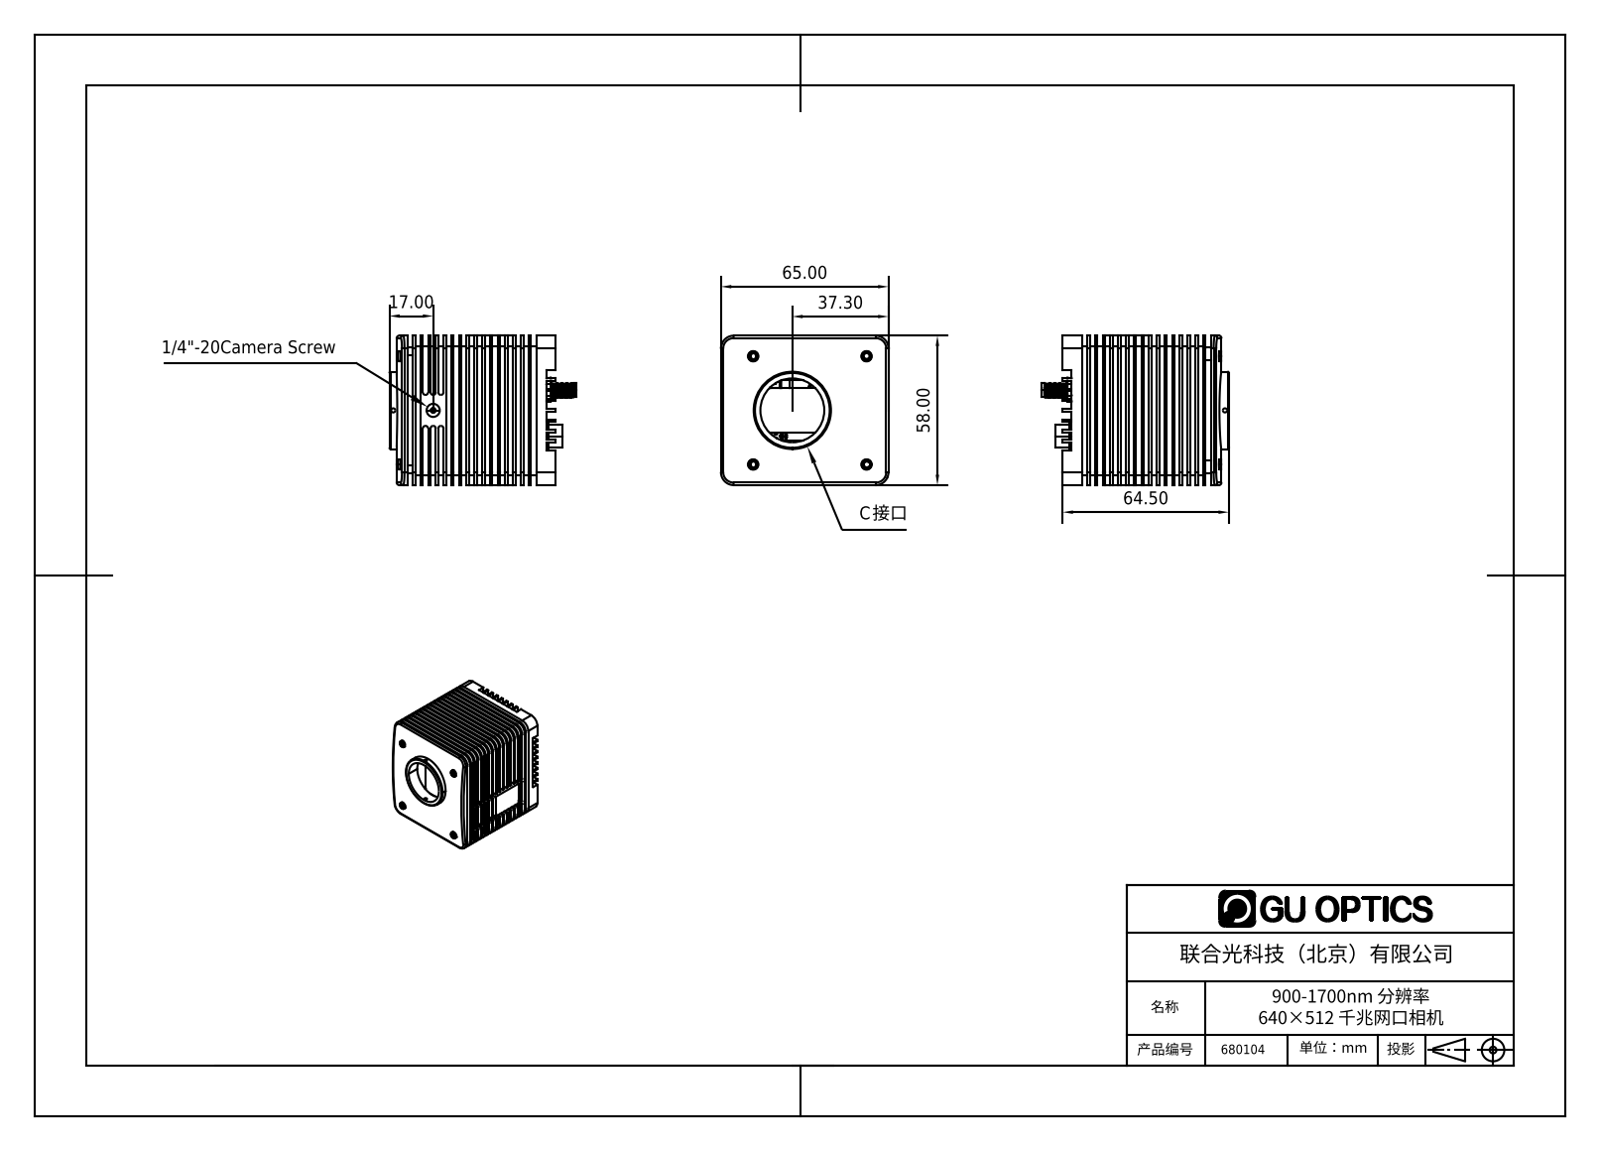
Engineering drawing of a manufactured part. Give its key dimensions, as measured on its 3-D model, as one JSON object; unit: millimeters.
{"part_name": "680103", "step_written_by": "SolidWorks 2020 (CONFIG_CONTROL_DESIGN)", "units": "millimeters", "bodies": {"solids": 34, "faces": 1819, "planar": 1117, "cylindrical": 546, "other": 156}, "overall_size": [72.6, 65, 58], "volume_mm3": 183381, "surface_area_mm2": 79241, "round_holes": [[0.8, 14], [2.2, 8], [4, 4], [5.7, 2], [6.6, 2], [7.4, 2], [7.8, 2], [8, 2], [8.1, 2], [0.5, 1], [0.6, 1], [1.6, 1]], "round_bosses_or_shafts": [[0.46, 10], [3.8, 8], [2, 8], [1.2, 8], [1.1, 6], [11, 2], [9.4, 2], [8.85, 2]], "partial_cylinders_radius": [[4.1, 24], [1, 10], [3, 10], [1.5, 6], [5, 6], [0.5, 5], [0.8, 5], [0.6, 4]], "face_to_face_distances": [3, 2, 6, 4, 9, 42, 33, 1, 5, 36], "hole_center_spacings": [1.8, 3.12, 1.6, 2.26, 1.81, 3.2, 3.6, 3.81]}
